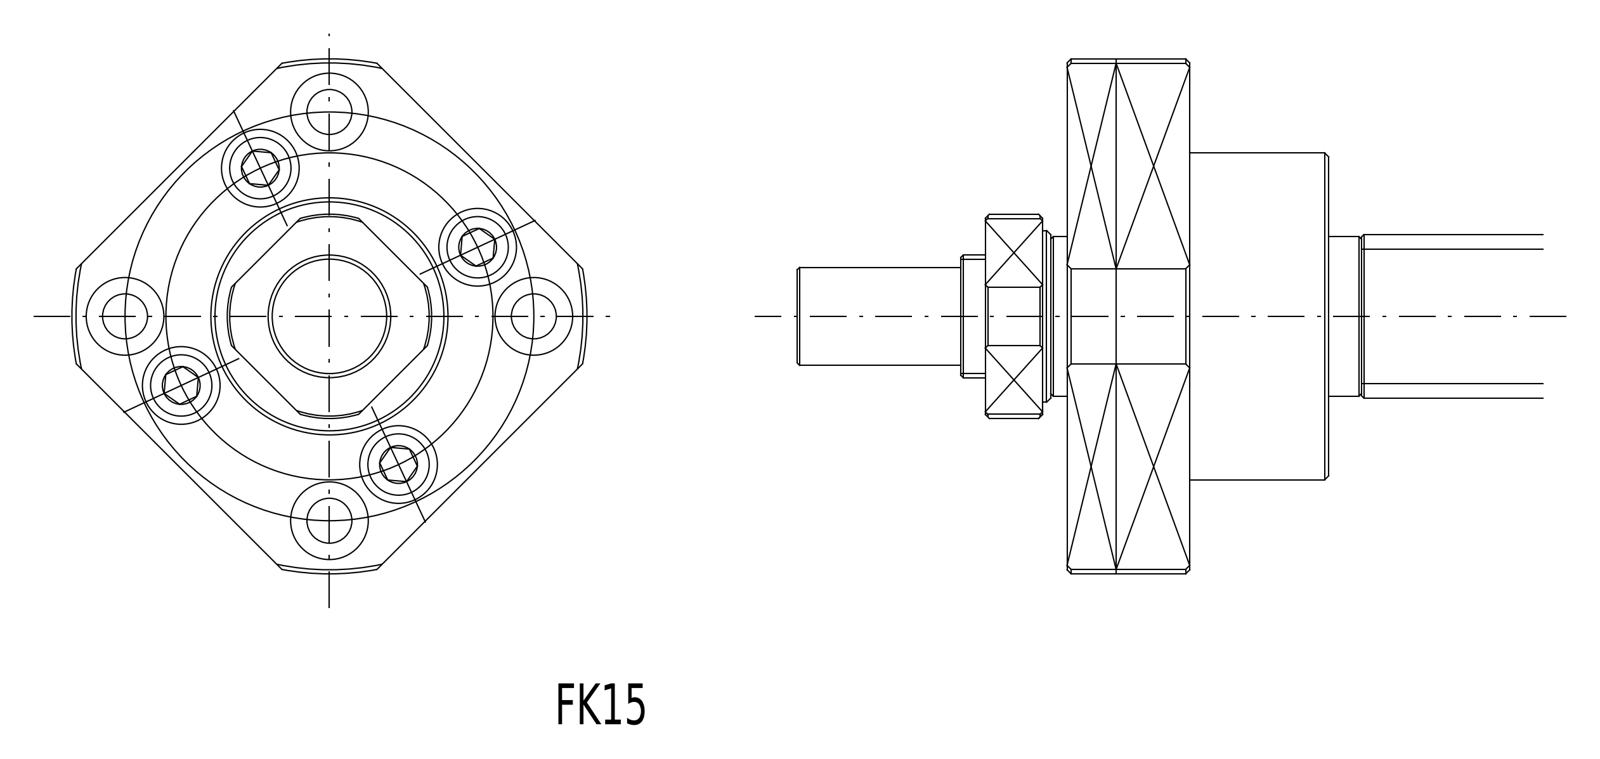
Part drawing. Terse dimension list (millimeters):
written by: SolidWorks 2008 (CONFIG_CONTROL_DESIGN)
unit: mm
bodies: 35 solids, 452 faces (66 planar, 130 cylindrical, 256 other)
size: 52 × 52 × 46
volume: 46 201 mm³; area: 33 000 mm²
holes: 6× ⌀3.3, 4× ⌀4.5, 4× ⌀5.5, 4× ⌀9.5, 1× ⌀14, 1× ⌀15, 1× ⌀20, 1× ⌀26, 1× ⌀26.15, 1× ⌀28, 1× ⌀28.5
bosses: 1× ⌀40, 1× ⌀39.4, 1× ⌀32, 1× ⌀22, 1× ⌀21, 1× ⌀19.5, 1× ⌀19
rounds: 1× R12.5, 1× R31.5
face distances: 9, 6, 15, 17, 26, 52, 2, 11, 8, 18
hole spacings: 10.9, 20, 24.55, 25, 28.28, 35.36, 38.05, 43.95
